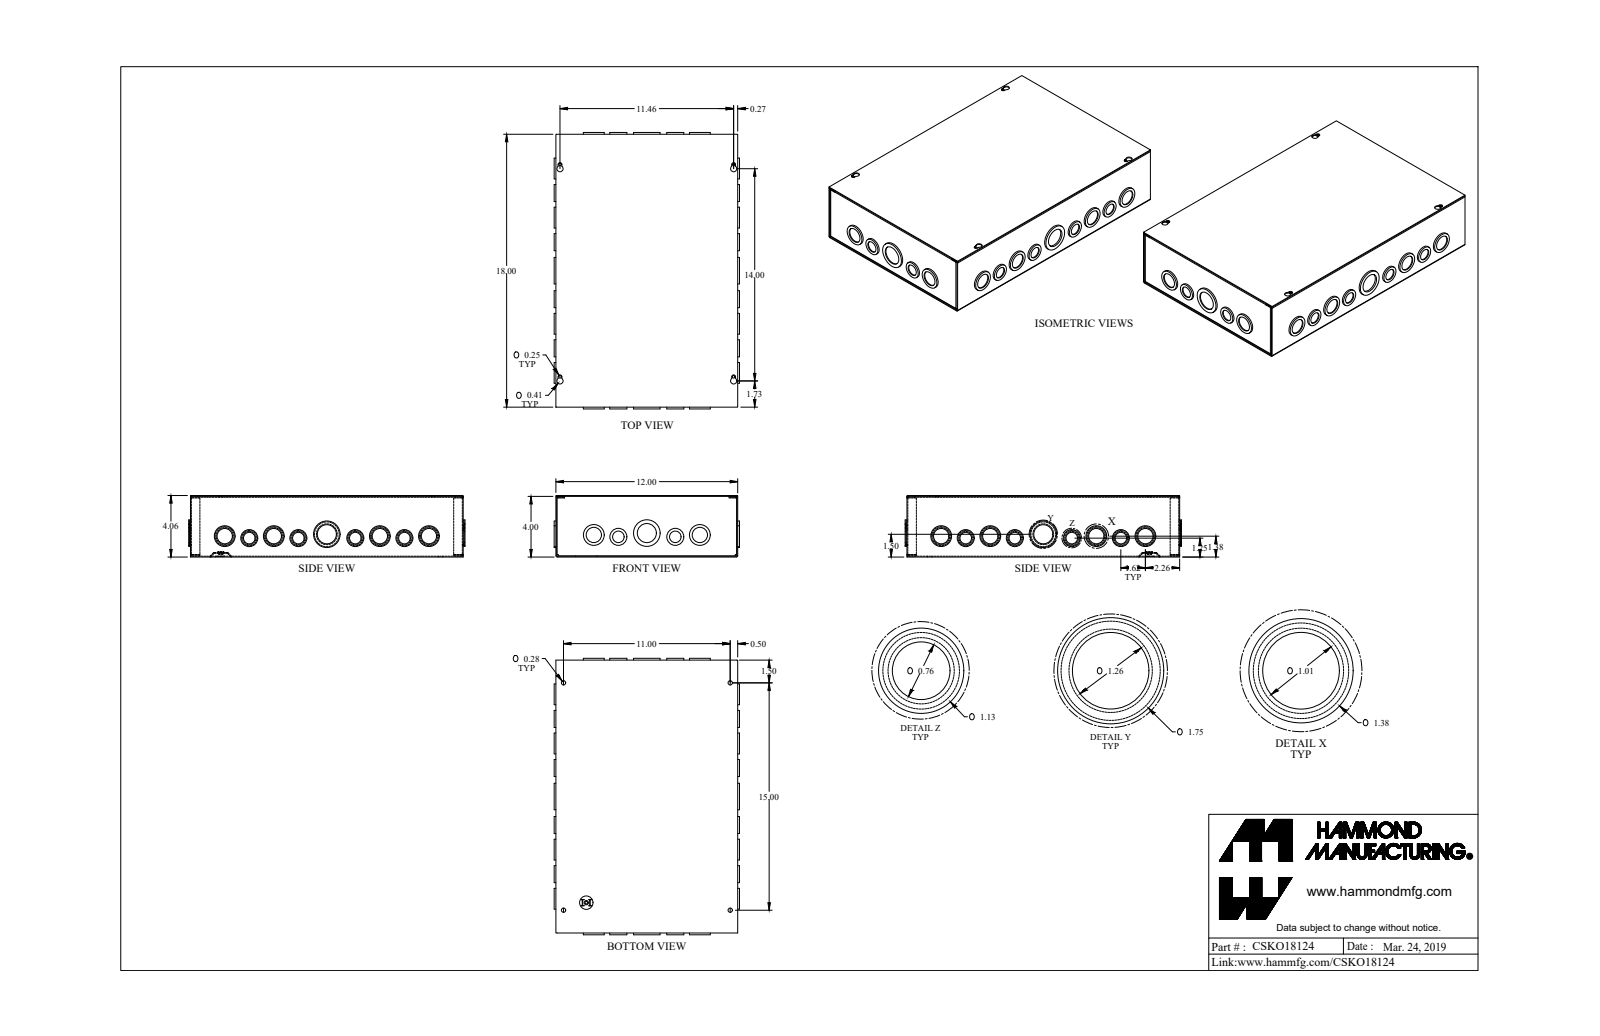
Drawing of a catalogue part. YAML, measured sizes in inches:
part_name: "CSKO18124_Default"
step_written_by: "SolidWorks 2019 (CONFIG_CONTROL_DESIGN)"
units: inches
bodies: {solids: 4, faces: 541, planar: 237, cylindrical: 296, other: 8}
overall_size: [18.234, 12.234, 4.057]
volume: 41.55
surface_area: 1471
round_holes:
  - {diameter: 1.011, count: 12}
  - {diameter: 1.261, count: 8}
  - {diameter: 0.761, count: 6}
  - {diameter: 0.17, count: 5}
  - {diameter: 0.281, count: 4}
  - {diameter: 1.636, count: 2}
  - {diameter: 0.5, count: 1}
round_bosses_or_shafts:
  - {diameter: 1.125, count: 10}
  - {diameter: 1.375, count: 7}
  - {diameter: 0.875, count: 6}
  - {diameter: 0.875, count: 6}
  - {diameter: 1.75, count: 2}
  - {diameter: 1.125, count: 2}
  - {diameter: 1.375, count: 1}
  - {diameter: 0.492, count: 1}
partial_cylinders:
  - {radius: 0.029, count: 12}
  - {radius: 0.086, count: 12}
  - {radius: 0.057, count: 8}
  - {radius: 0.125, count: 4}
  - {radius: 0.203, count: 4}
face_to_face_distances: [0.057, 4, 3.943, 4.057, 11.943, 12, 17.943, 11.886, 18, 0.114]
hole_center_spacings: [1.625, 0.55, 1.896, 3.24, 3.502, 5.381, 7, 8.621]
